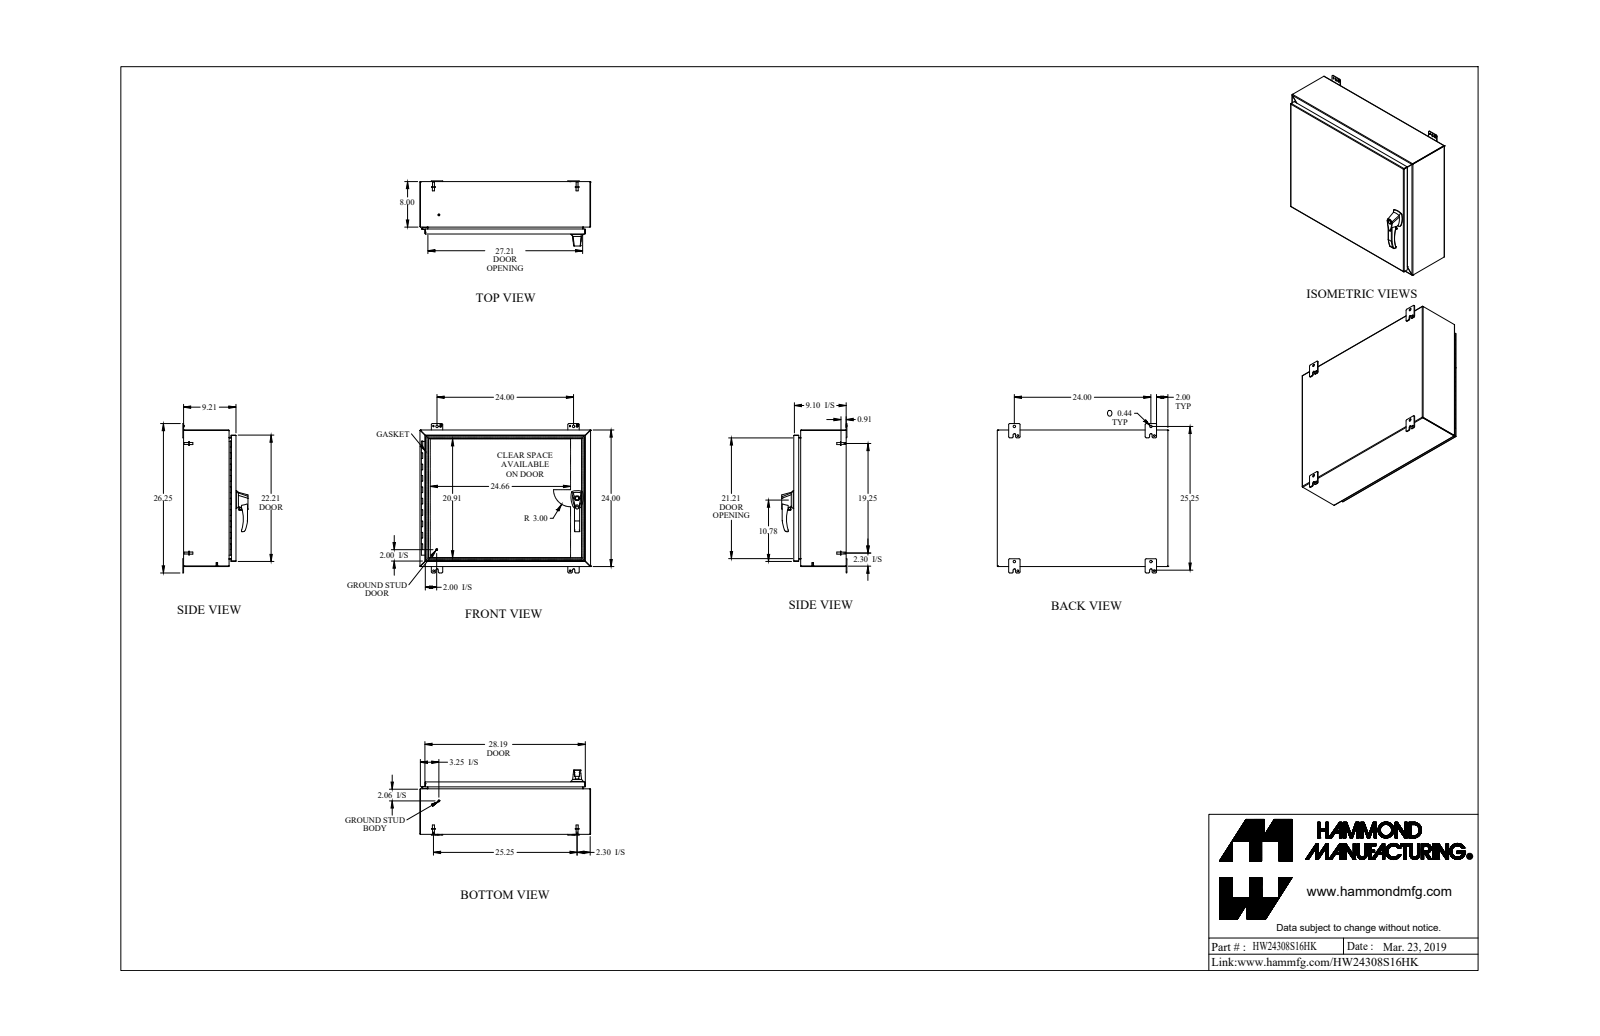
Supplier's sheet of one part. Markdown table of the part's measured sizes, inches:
| quantity | value |
| --- | --- |
| part name | HW24308S16HK |
| STEP written by | SolidWorks 2018 (AUTOMOTIVE_DESIGN) |
| units | inches |
| bodies | 46 solids, 1401 faces (670 planar, 579 cylindrical, 152 other) |
| overall size | 30 × 26.25 × 11.45 |
| volume | 217.9 in³ |
| surface area | 5 659 in² |
| round holes (diameter × count) | 0.176 × 6, 0.313 × 5, 0.25 × 3, 0.265 × 3, 0.413 × 3, 0.196 × 2, 0.256 × 2, 0.394 × 2, 0.437 × 2, 0.11 × 1, 0.233 × 1, 0.33 × 1 |
| round bosses / shafts (diameter × count) | 0.375 × 9, 0.25 × 7, 0.156 × 6, 0.65 × 4, 0.332 × 4, 0.313 × 4, 1 × 3, 0.51 × 3 |
| partial cylindrical surfaces (radius × count) | 0.25 × 27, 0.188 × 24, 0.036 × 20, 0.108 × 20, 0.06 × 12, 0.125 × 9, 0.045 × 8, 0.218 × 8 |
| main face-to-face distances | 0.072, 0.072, 9.138, 9.066, 9.138, 9.21, 23.928, 29.928, 7.928, 23.856 |
| hole center spacings | 1.111, 8.118, 8.119, 16.237, 1.338, 6.78, 7.576, 7.577 |
